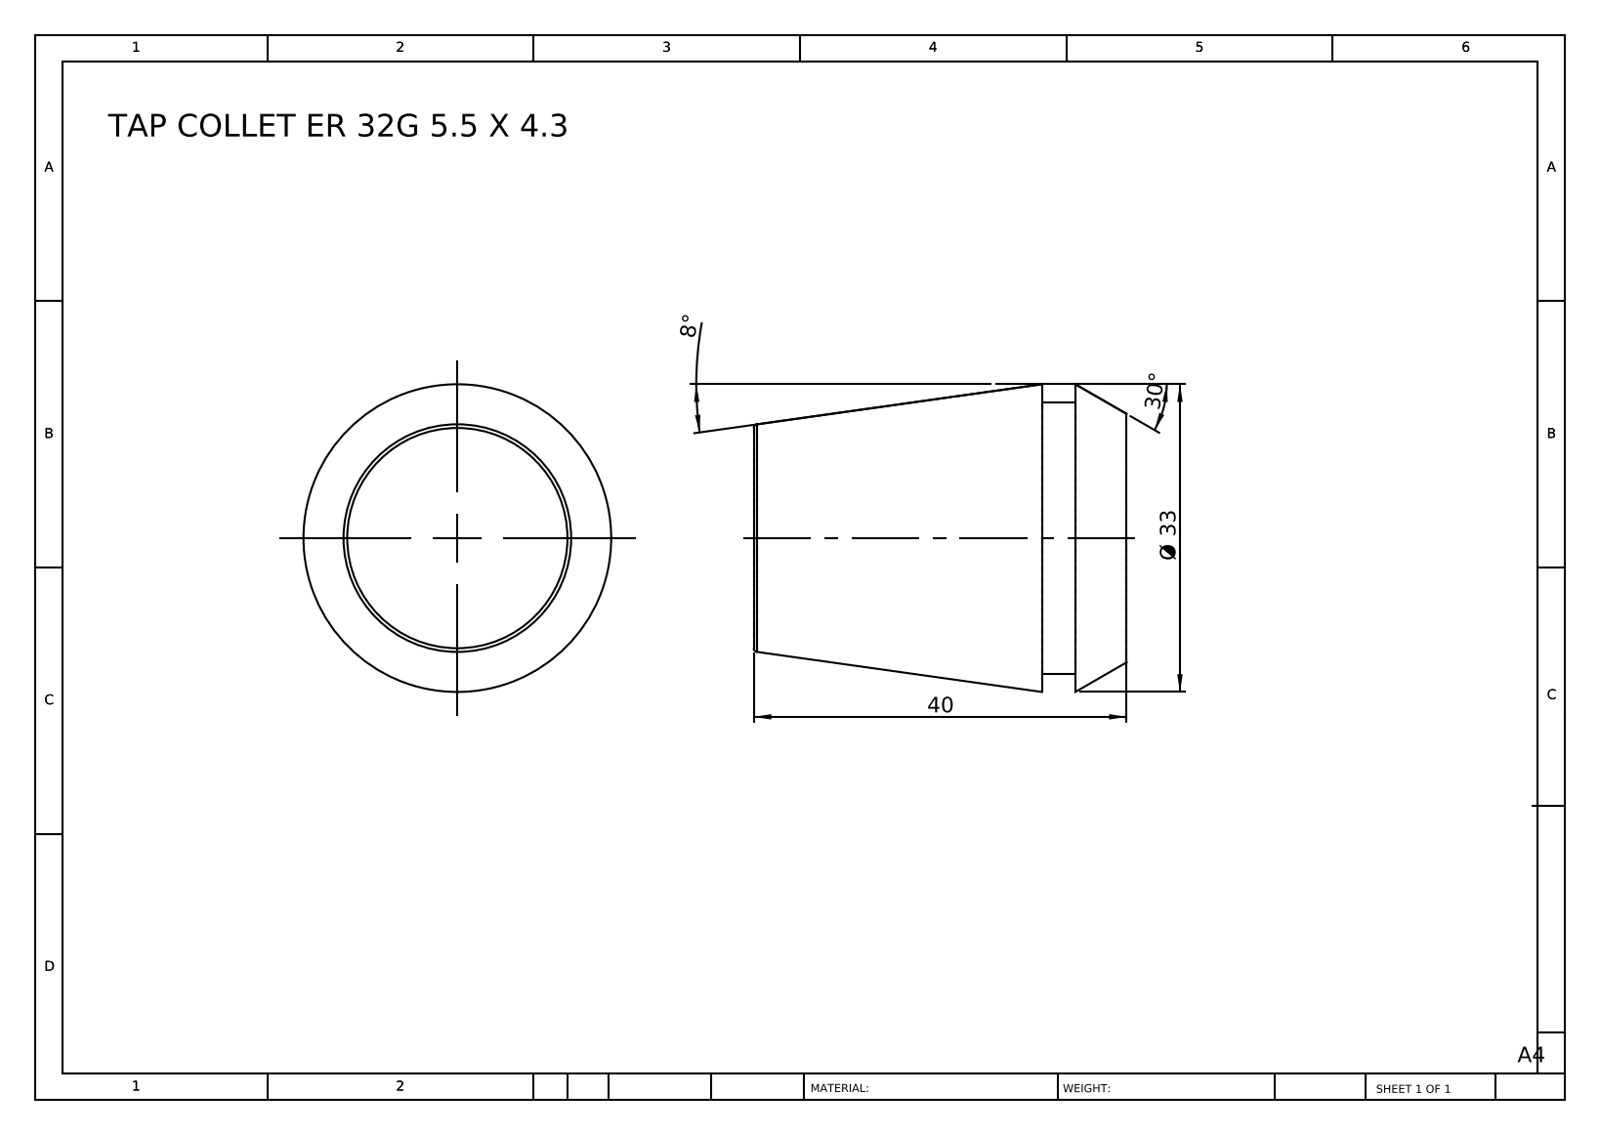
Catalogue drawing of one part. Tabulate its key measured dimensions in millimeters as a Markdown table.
| quantity | value |
| --- | --- |
| part name | TAP COLLET ER 32G 5.5 X 4.3 |
| STEP written by | SolidWorks 2014 (CONFIG_CONTROL_DESIGN) |
| units | millimeters |
| bodies | 1 solid, 12 faces (4 planar, 2 cylindrical, 6 other) |
| overall size | 40 × 33 × 33 |
| volume | 26 350 mm³ |
| surface area | 5 119 mm² |
| round bosses / shafts (diameter × count) | 29.2 × 1 |
| main face-to-face distances | 40, 9.1, 30.9, 5.5, 3.6, 34.5 |
